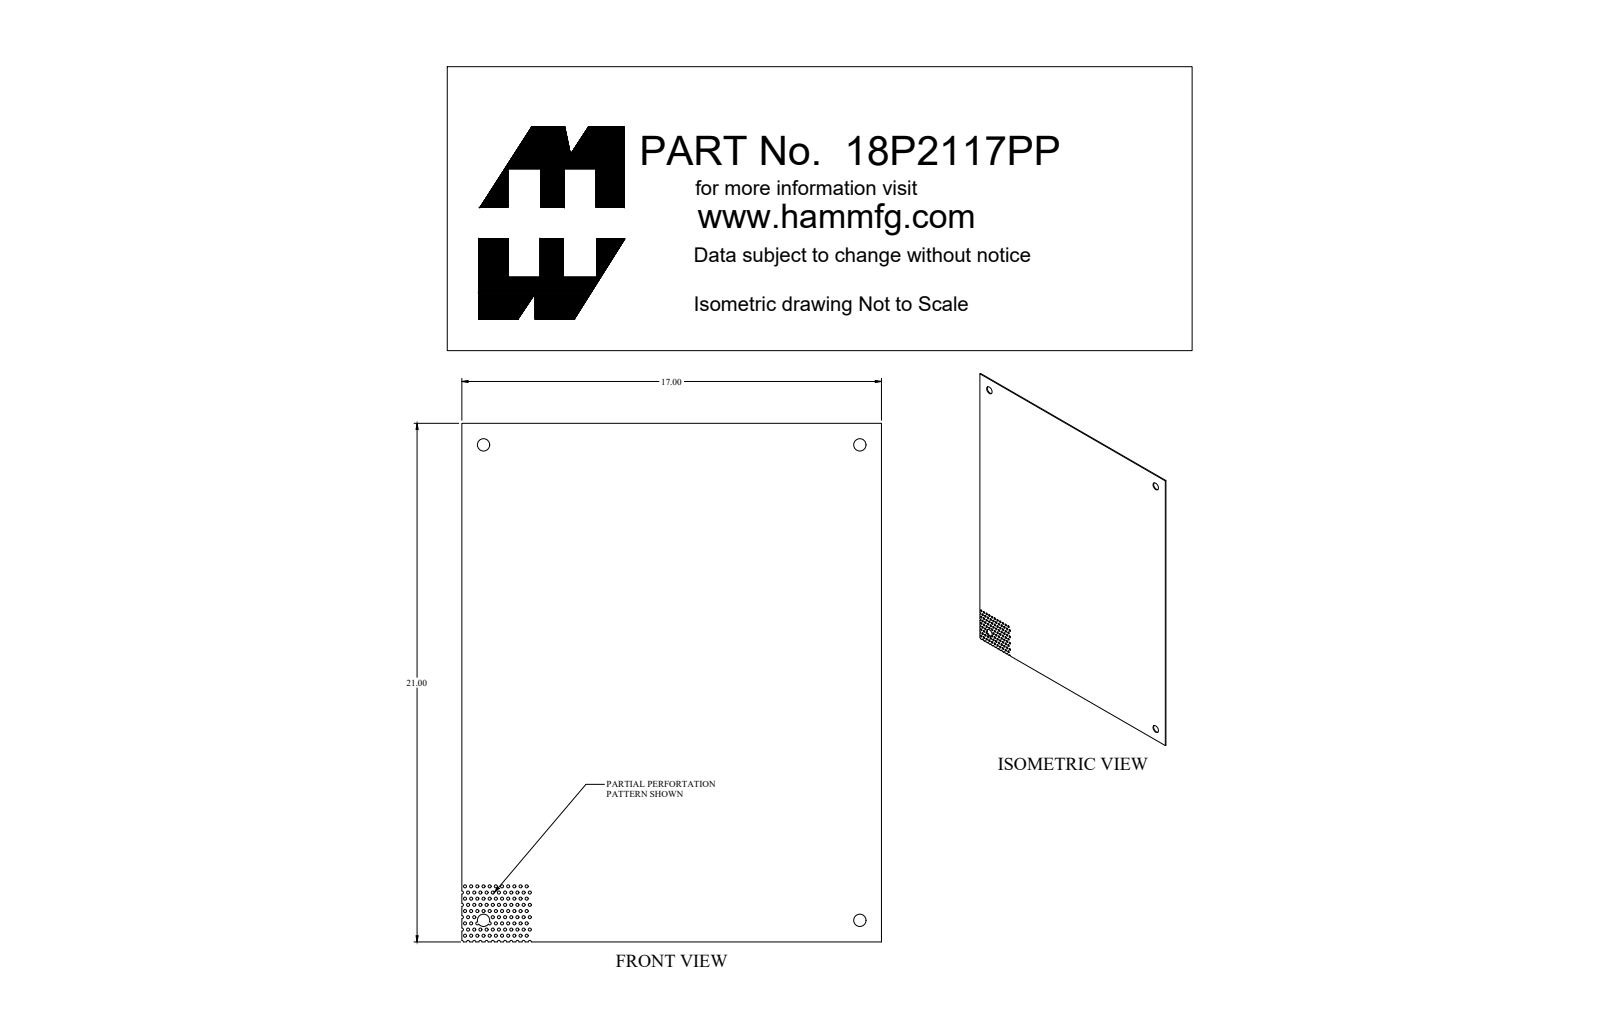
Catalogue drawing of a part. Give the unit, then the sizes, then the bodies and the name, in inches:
Units: inches
Overall size (bounding box): 21 × 17 × 0.057
Round holes (diameter × count): ⌀0.125 ×72, ⌀0.125 ×22, ⌀0.5 ×4
Partial cylindrical surfaces — rounded edges, fillets, slot ends (radius × count): R0.063 ×13, R0.062 ×5
Main face-to-face distances: 0.057, 17, 21
Hole centre spacings: 0.28, 0.5, 0.25, 0.673, 0.451, 0.75, 0.91, 1.153
Volume: 20.23 in³ · Surface area: 716.8 in²
Bodies: 1 solid, 251 faces (21 planar, 230 cylindrical, 0 other)
Part name (STEP PRODUCT): 18P2117PP_Default
STEP written by: SolidWorks 2018 (CONFIG_CONTROL_DESIGN)
